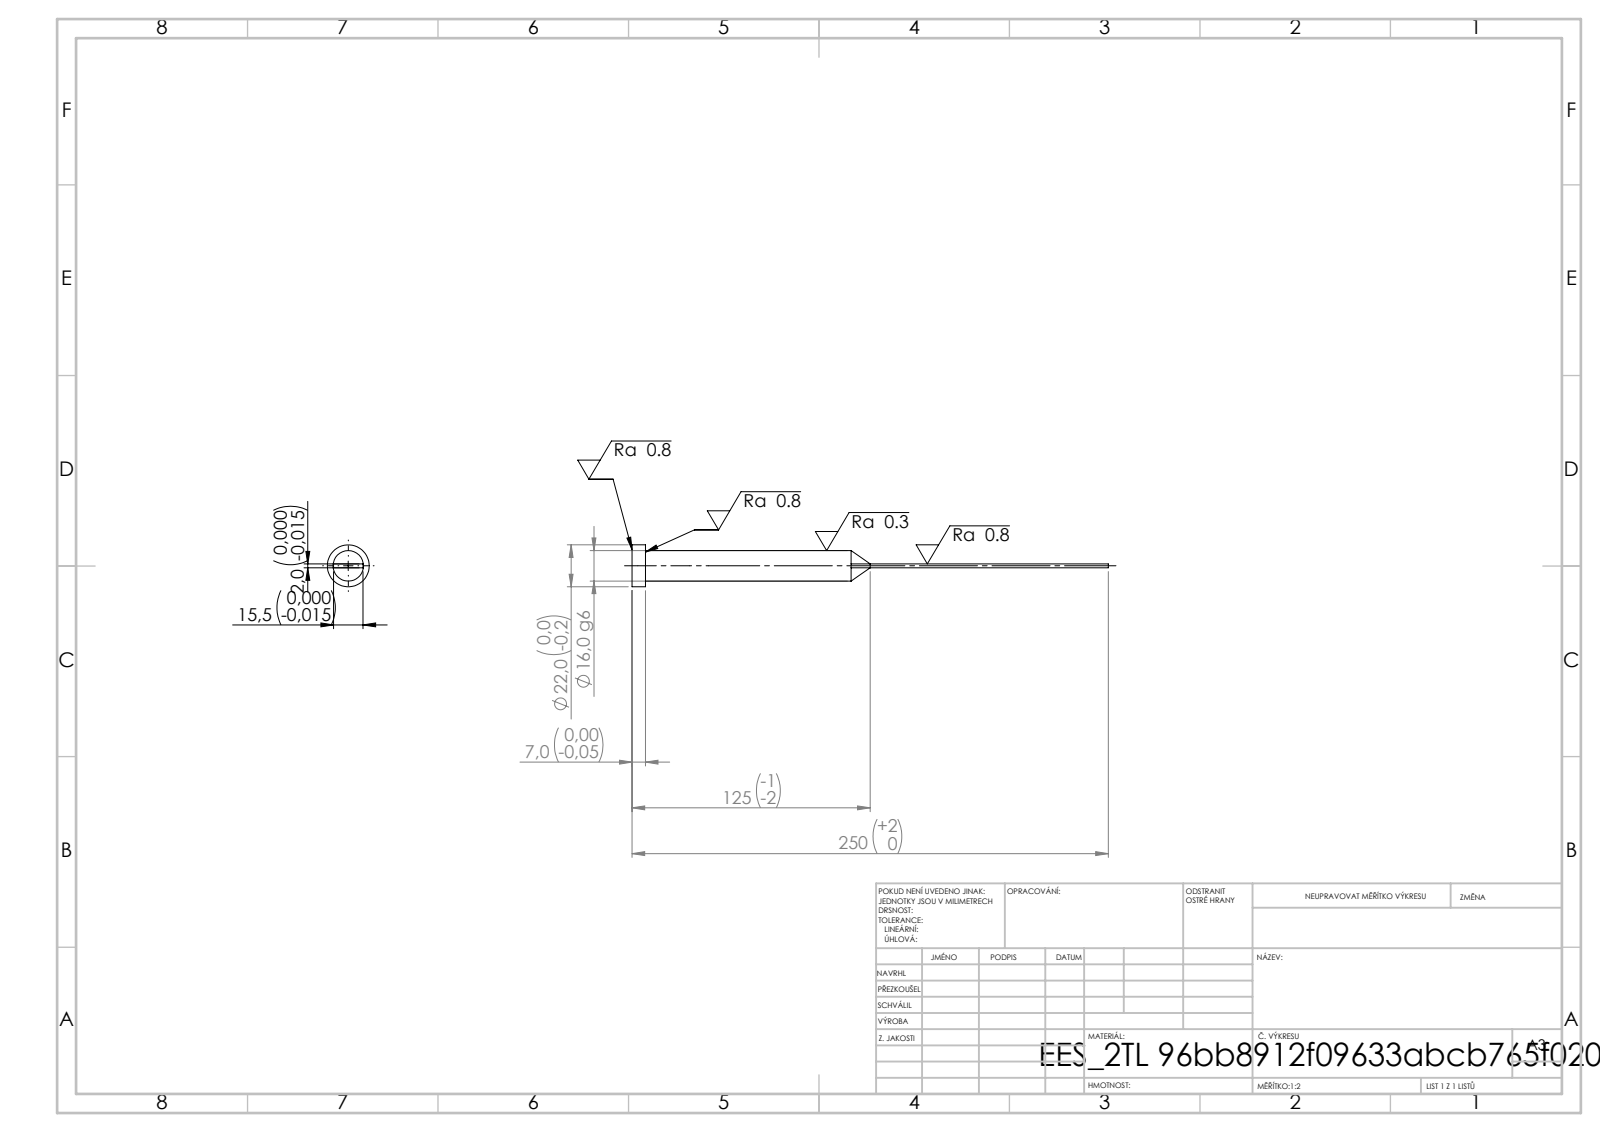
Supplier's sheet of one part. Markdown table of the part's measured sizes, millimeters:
| quantity | value |
| --- | --- |
| STEP written by | SolidWorks 2019 (CONFIG_CONTROL_DESIGN) |
| units | millimeters |
| bodies | 1 solid, 15 faces (7 planar, 4 cylindrical, 4 other) |
| overall size | 250 × 22 × 22 |
| volume | 29 342 mm³ |
| surface area | 11 325 mm² |
| round bosses / shafts (diameter × count) | 22 × 1, 16 × 1 |
| main face-to-face distances | 2, 15.5, 7, 250, 243 |
